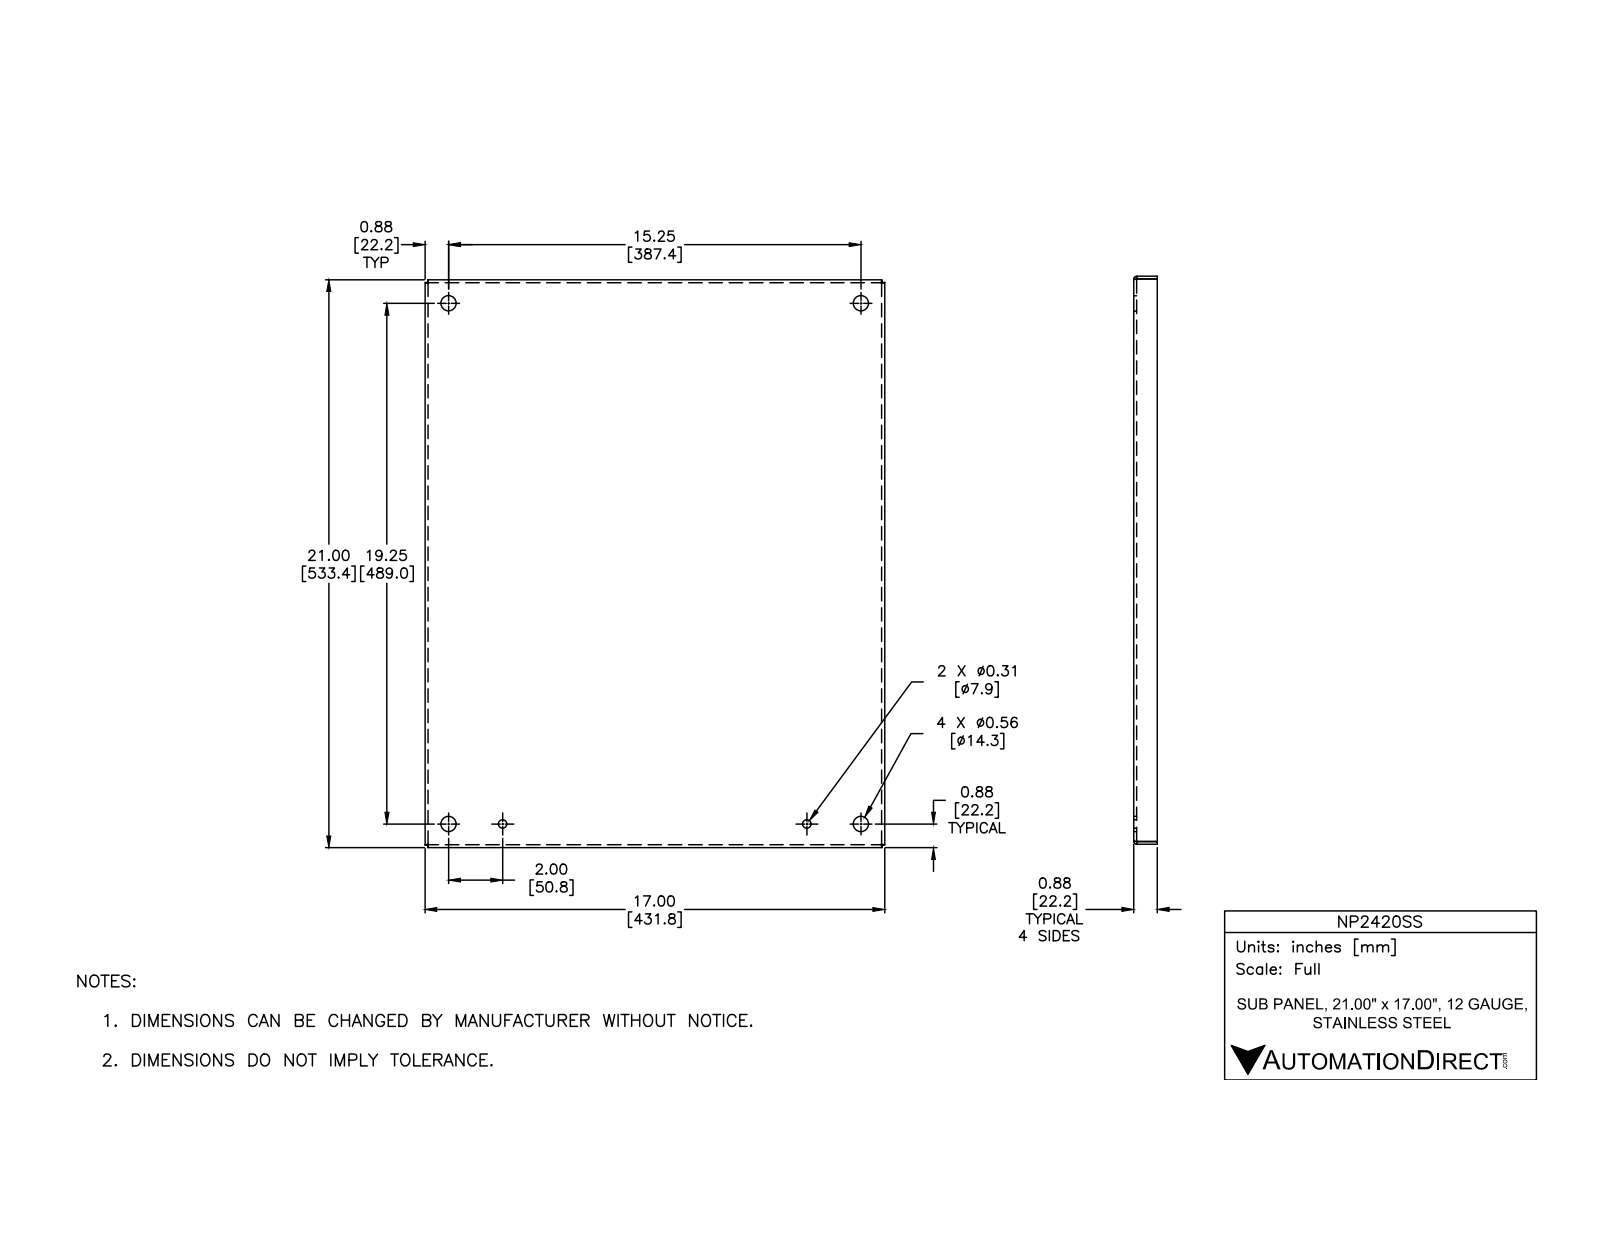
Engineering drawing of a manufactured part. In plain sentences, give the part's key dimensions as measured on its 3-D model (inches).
The part is named "NP2420SS". Its 3-D file was written by "Autodesk Inventor 2012 (AUTOMOTIVE_DESIGN)". It is 1 solid with 44 faces: 22 planar, 14 cylindrical and 8 other. Overall it measures 21 by 17 by 0.875 inches. Its volume is 38.6 cubic inches and its surface area 832.6 square inches. Round holes: 4 of diameter 0.563, 2 of diameter 0.312. Partial cylindrical surfaces (rounded edges, fillets, slot ends): 4 of radius 0.031, 4 of radius 0.125. The main face-to-face distances are 0.094, 16.906, 20.906, 17, 16.813, 21, 20.813, 0.781, 0.875, 0.105. The hole center spacings are 15.25, 19.25, 19.354, 24.559, 2, 2, 11.25, 13.25.
